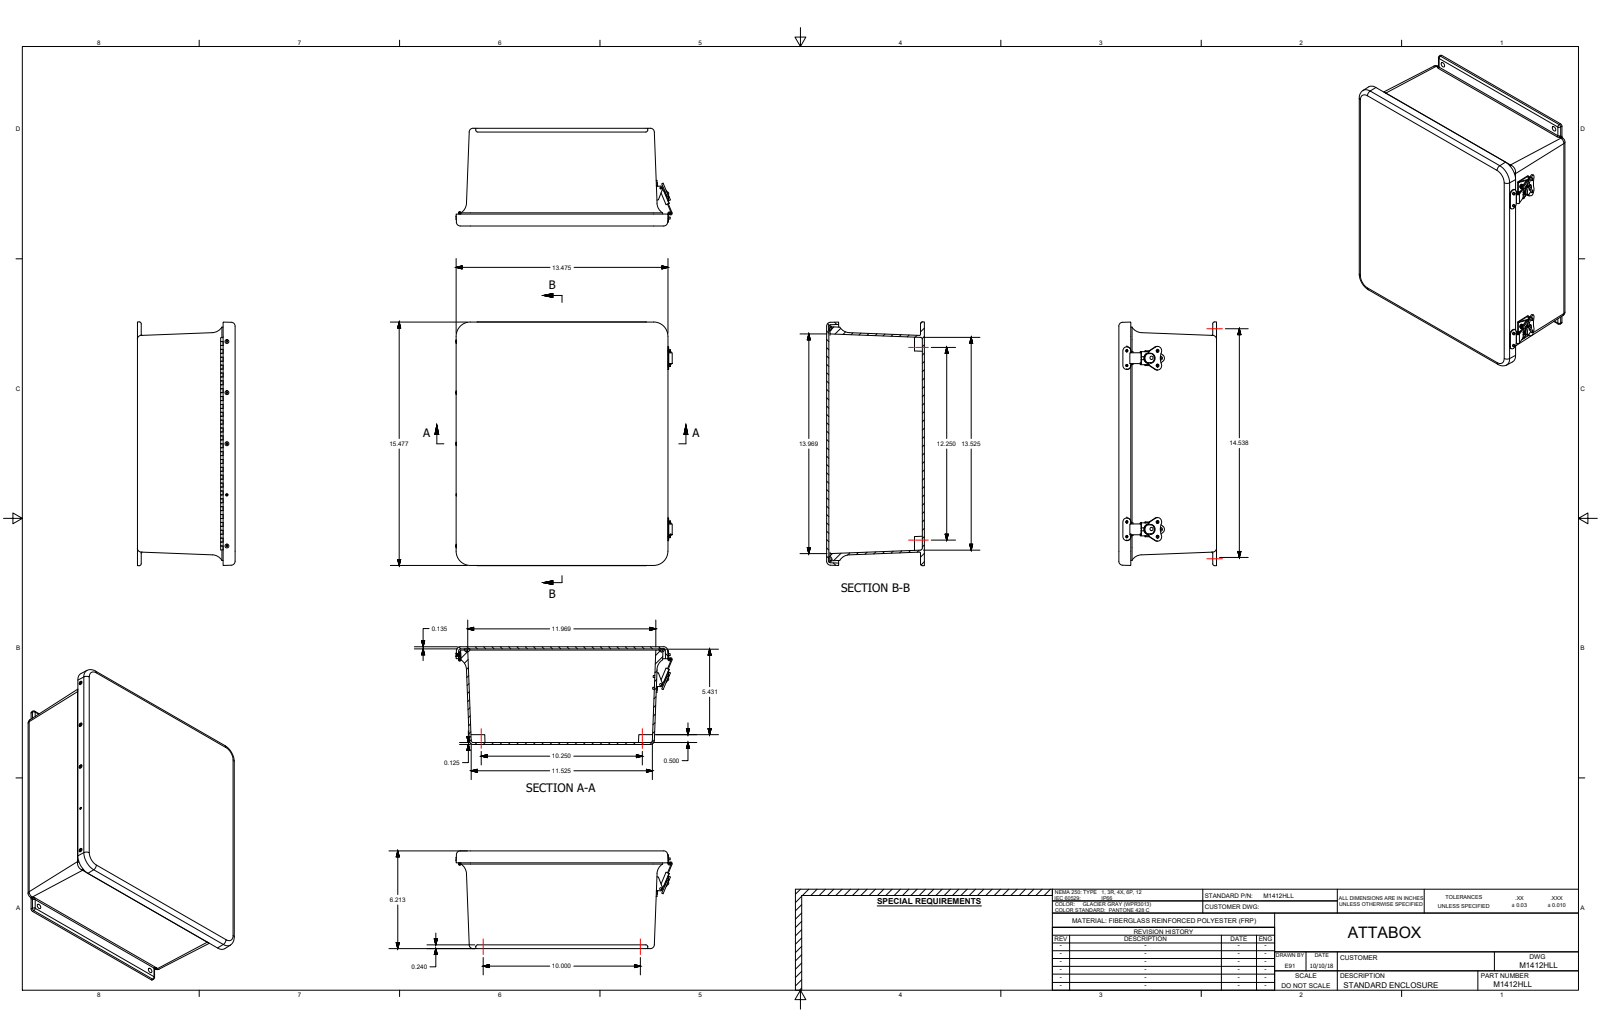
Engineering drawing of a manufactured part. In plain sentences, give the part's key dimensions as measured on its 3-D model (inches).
The part is named "M1412HLL". Its 3-D file was written by "SolidWorks 2018 (AUTOMOTIVE_DESIGN)". It is 44 solids with 1050 faces: 503 planar, 429 cylindrical and 118 other. Overall it measures 15.5 by 13.684 by 6.213 inches. Its volume is 113.8 cubic inches and its surface area 1 606 square inches. Round holes: 20 of diameter 0.14, 18 of diameter 0.104, 10 of diameter 0.131, 8 of diameter 0.152, 4 of diameter 0.13, 4 of diameter 0.133, 4 of diameter 0.187, 4 of diameter 0.218, 4 of diameter 0.312, 2 of diameter 0.135, 2 of diameter 0.189, 2 of diameter 0.191. Round bosses or shafts: 13 of diameter 0.125, 7 of diameter 0.125, 2 of diameter 0.66, 2 of diameter 0.582, 2 of diameter 0.525, 2 of diameter 0.286, 2 of diameter 0.213, 2 of diameter 0.18. Partial cylindrical surfaces (rounded edges, fillets, slot ends): 17 of radius 0.125, 16 of radius 0.015, 13 of radius 0.06, 10 of radius 0.25, 8 of radius 0.011, 8 of radius 0.02, 8 of radius 0.055, 8 of radius 0.07. The main face-to-face distances are 0.125, 0.135, 6.213, 6.078, 6.087, 5.953, 0.125, 0.33, 0.152, 0.213. The hole center spacings are 3.25, 6.5, 9.75, 10.882, 10.881, 0.937, 0.013, 0.25.
